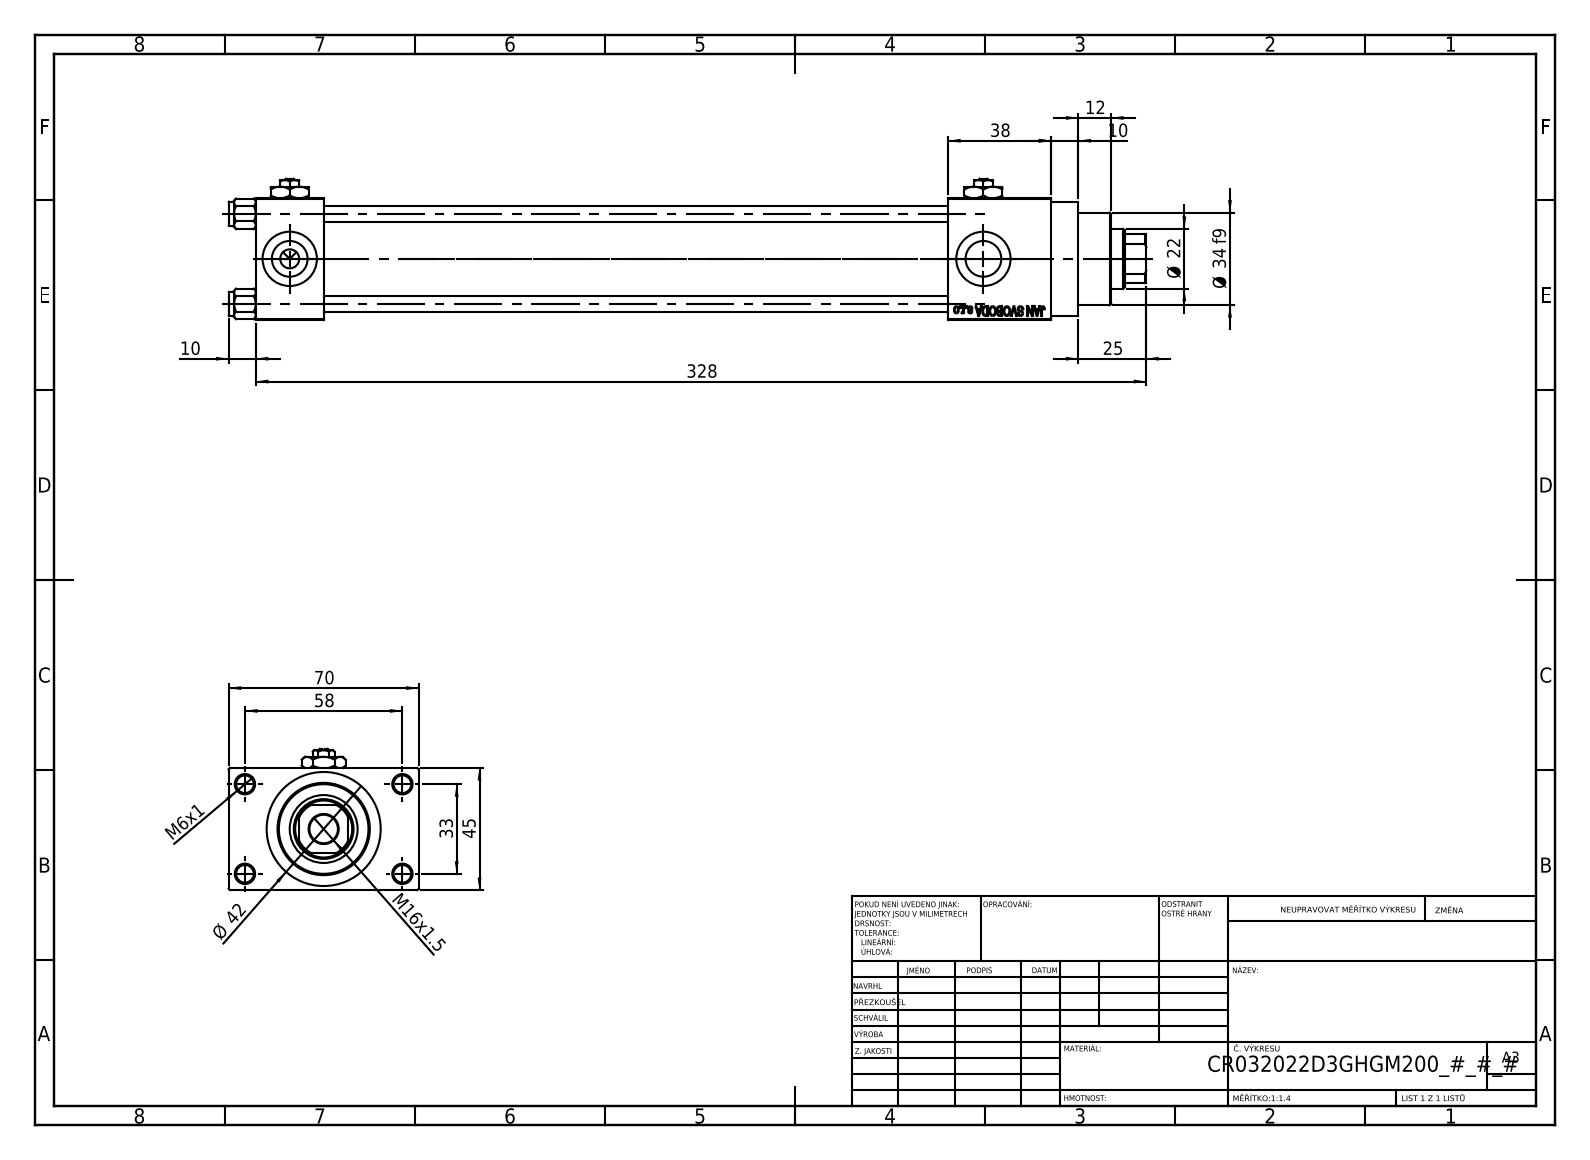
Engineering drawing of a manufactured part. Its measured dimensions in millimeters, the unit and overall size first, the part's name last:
Units: millimetres
Overall size (bounding box): 338 × 70 × 52
Round holes (diameter × count): ⌀6 ×4, ⌀6.5 ×4, ⌀13.16 ×4, ⌀20 ×4, ⌀7 ×3, ⌀10.5 ×1, ⌀22 ×1, ⌀24 ×1, ⌀25 ×1, ⌀32 ×1, ⌀33 ×1
Round bosses / shafts (diameter × count): ⌀9 ×4, ⌀42 ×1, ⌀38 ×1, ⌀34 ×1
Partial cylindrical surfaces — rounded edges, fillets, slot ends (radius × count): R10.5 ×1
Main face-to-face distances: 45, 25, 12.5, 230, 255, 57.5, 268, 38, 293, 70
Hole centre spacings: 12.4, 23.48, 33.2, 33.37, 35.35, 45.6, 56.35, 33
Volume: 389 902 mm³ · Surface area: 147 308 mm²
Bodies: 13 solids, 1201 faces (542 planar, 99 cylindrical, 560 other)
Part name (STEP PRODUCT): V215CR_D_TYCINKA; V215CR_VCP_D; V215_VC_A; Zatka_pro_OIL_PORT (+2 more)
STEP written by: SolidWorks 2019 (CONFIG_CONTROL_DESIGN)
